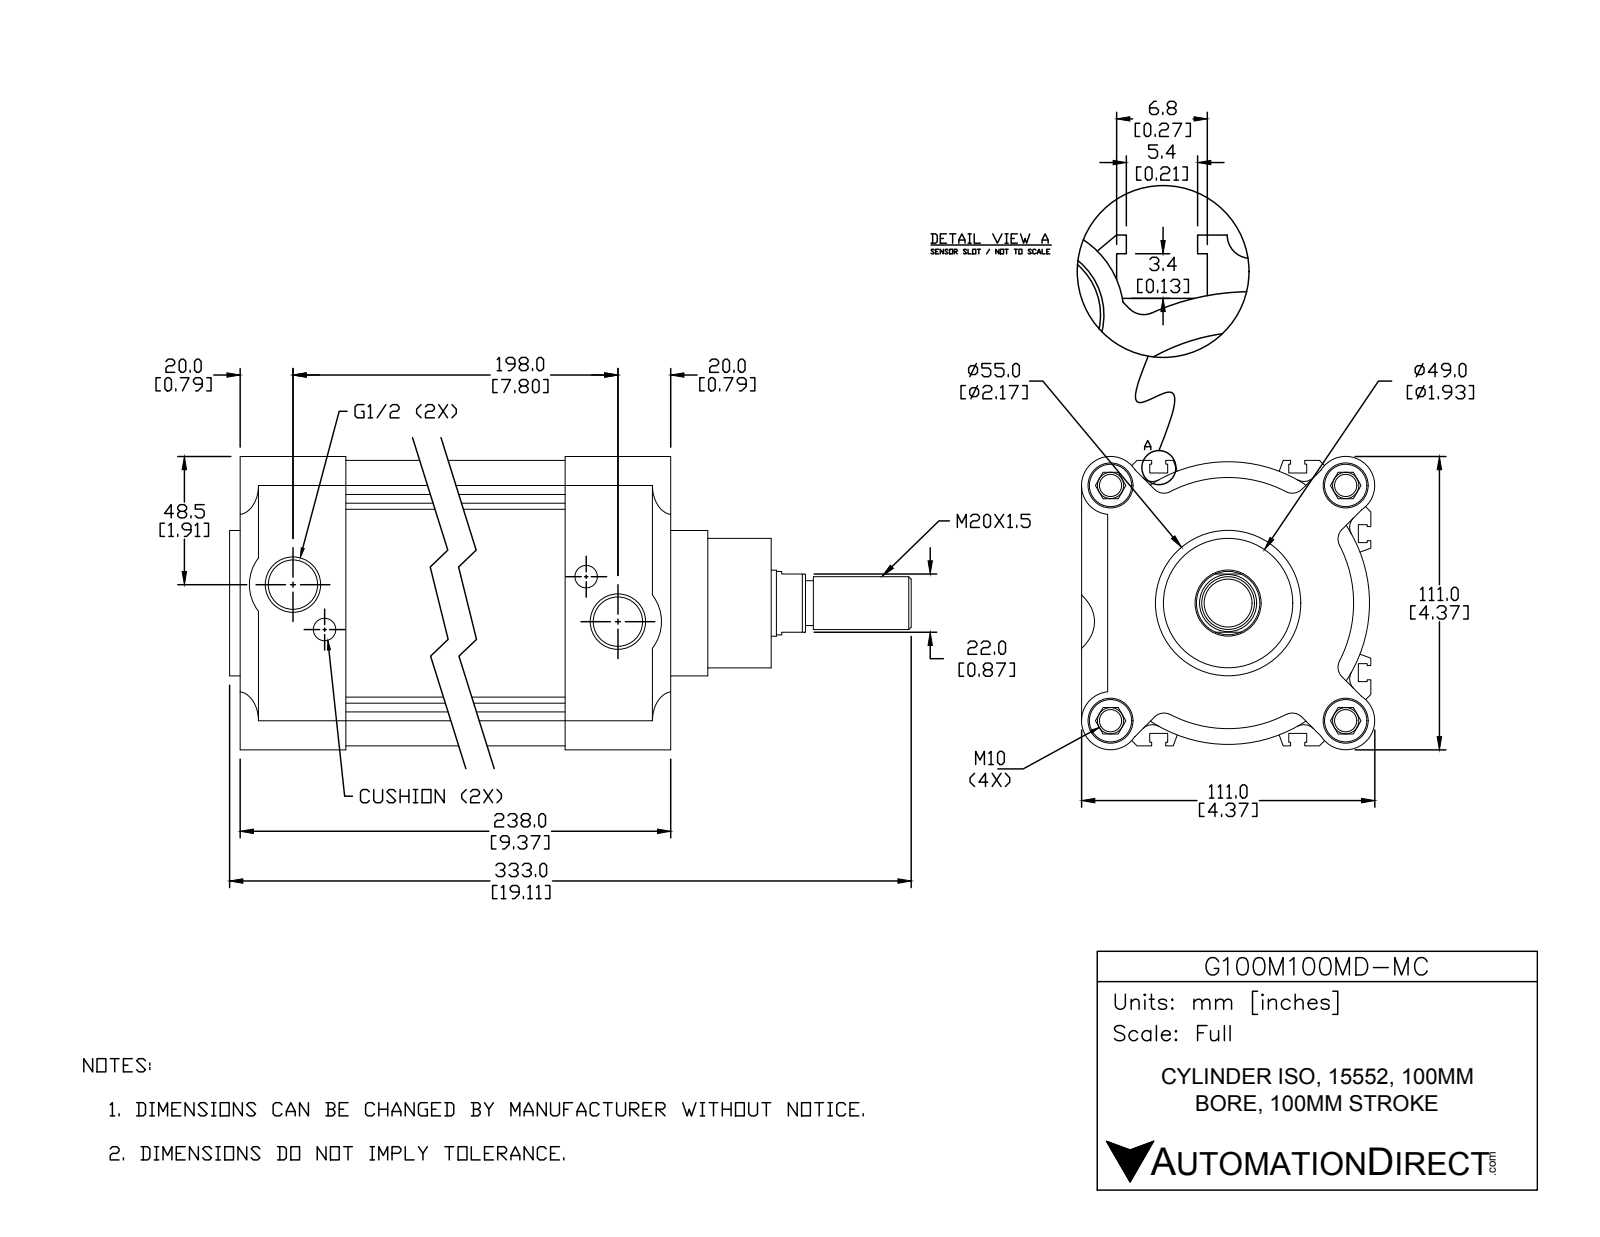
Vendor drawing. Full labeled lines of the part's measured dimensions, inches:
Part name (STEP PRODUCT): 100121100-R; 100121-HR; G100M100MD-MC; 100-100-120.5-B (+1 more)
STEP written by: SolidWorks 2015 (CONFIG_CONTROL_DESIGN)
Units: inches
Bodies: 4 solids, 462 faces (248 planar, 162 cylindrical, 52 other)
Overall size (bounding box): 13.11 × 4.37 × 4.37
Volume: 116.8 in³ · Surface area: 484.9 in²
Round holes (diameter × count): ⌀0.33 ×4, ⌀0.669 ×4, ⌀0.335 ×2, ⌀0.734 ×2, ⌀0.984 ×1
Round bosses / shafts (diameter × count): ⌀0.63 ×4, ⌀3.937 ×1, ⌀2.165 ×1, ⌀1.929 ×1, ⌀0.945 ×1, ⌀0.787 ×1, ⌀0.669 ×1
Partial cylindrical surfaces — rounded edges, fillets, slot ends (radius × count): R0.197 ×12, R0.004 ×6, R0.374 ×4, R0.433 ×4, R0.65 ×2, R1.87 ×1, R2.087 ×1, R2.106 ×1
Main face-to-face distances: 7.402, 0.394, 5.827, 1.575, 1.969, 7.795, 1.496, 3.465, 5.433, 3.937
Hole centre spacings: 2.478, 3.504, 0.819, 4.956, 7.324, 6.896, 7.815
